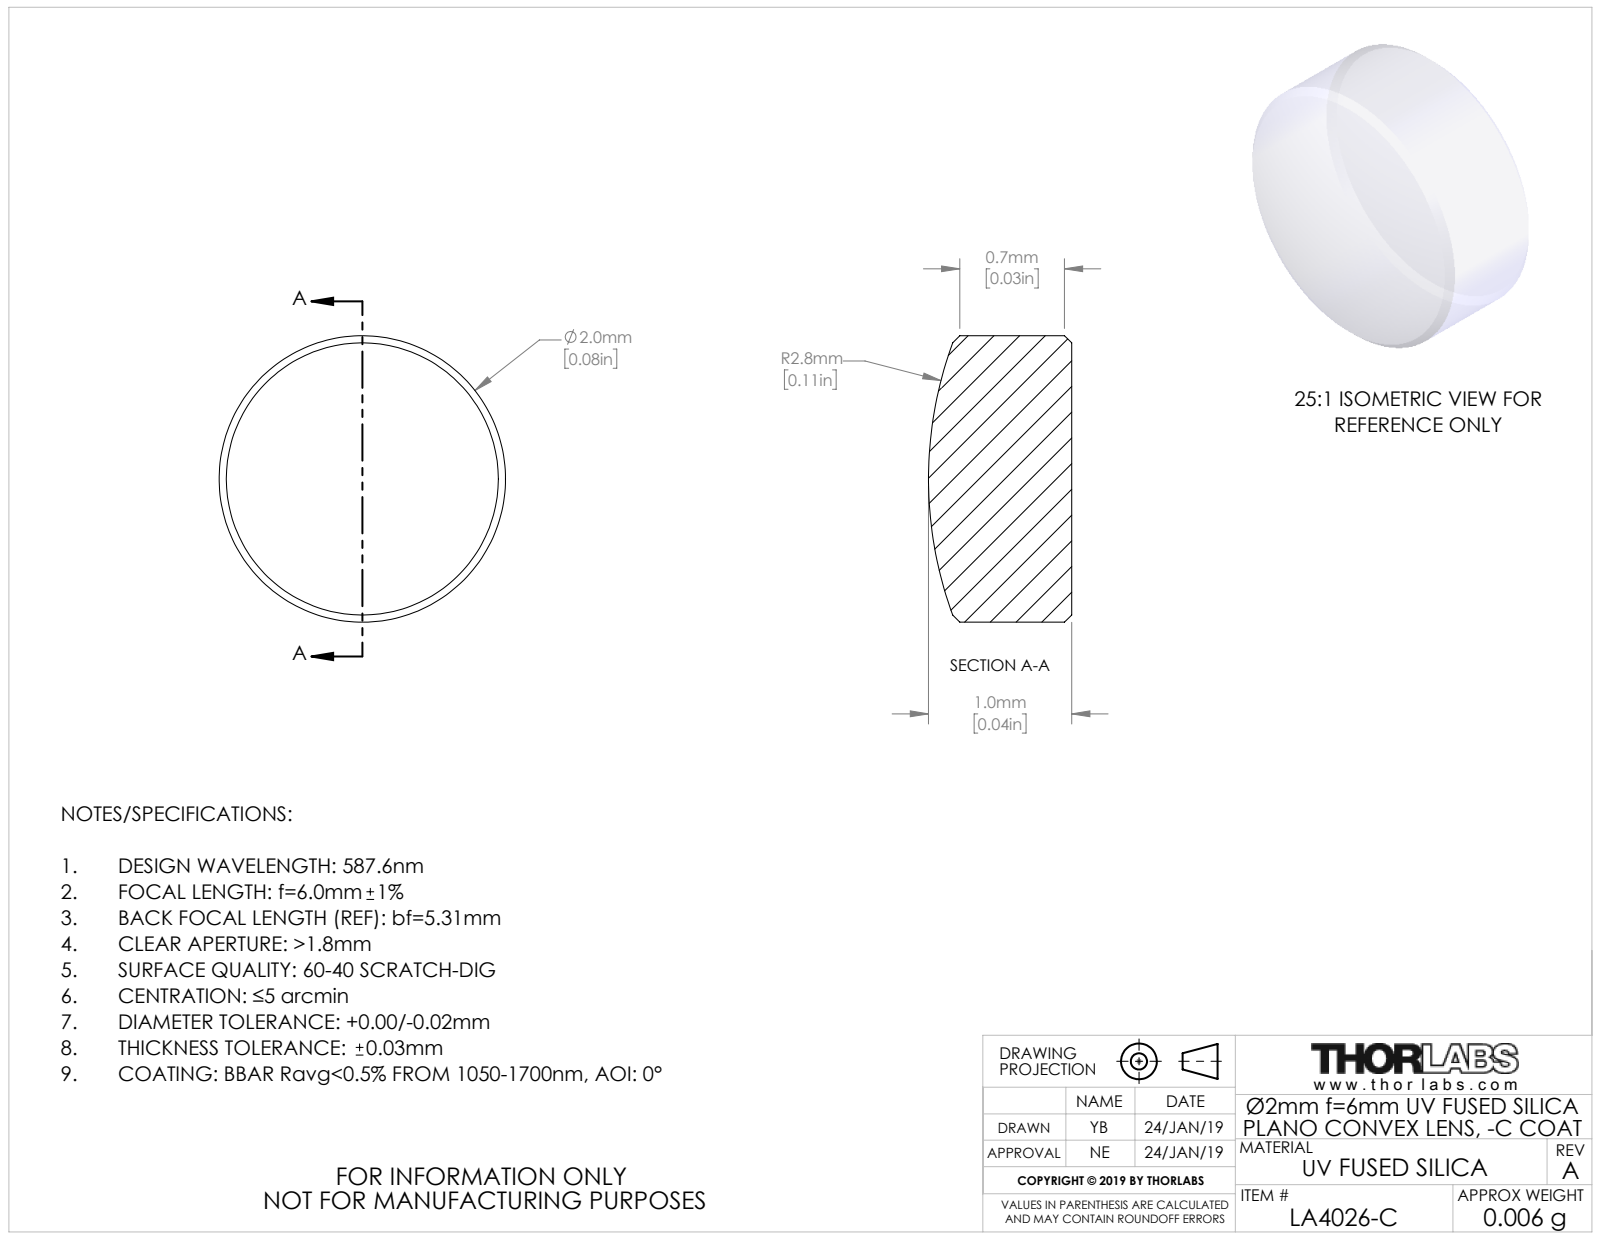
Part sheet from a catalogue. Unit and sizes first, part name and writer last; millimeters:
Units: millimetres
Overall size (bounding box): 2 × 2 × 1
Round bosses / shafts (diameter × count): ⌀2 ×1
Volume: 3 mm³ · Surface area: 11 mm²
Bodies: 1 solid, 9 faces (1 planar, 2 cylindrical, 6 other)
Part name (STEP PRODUCT): TTN162821-E0W
STEP written by: SolidWorks 2018 (CONFIG_CONTROL_DESIGN)
